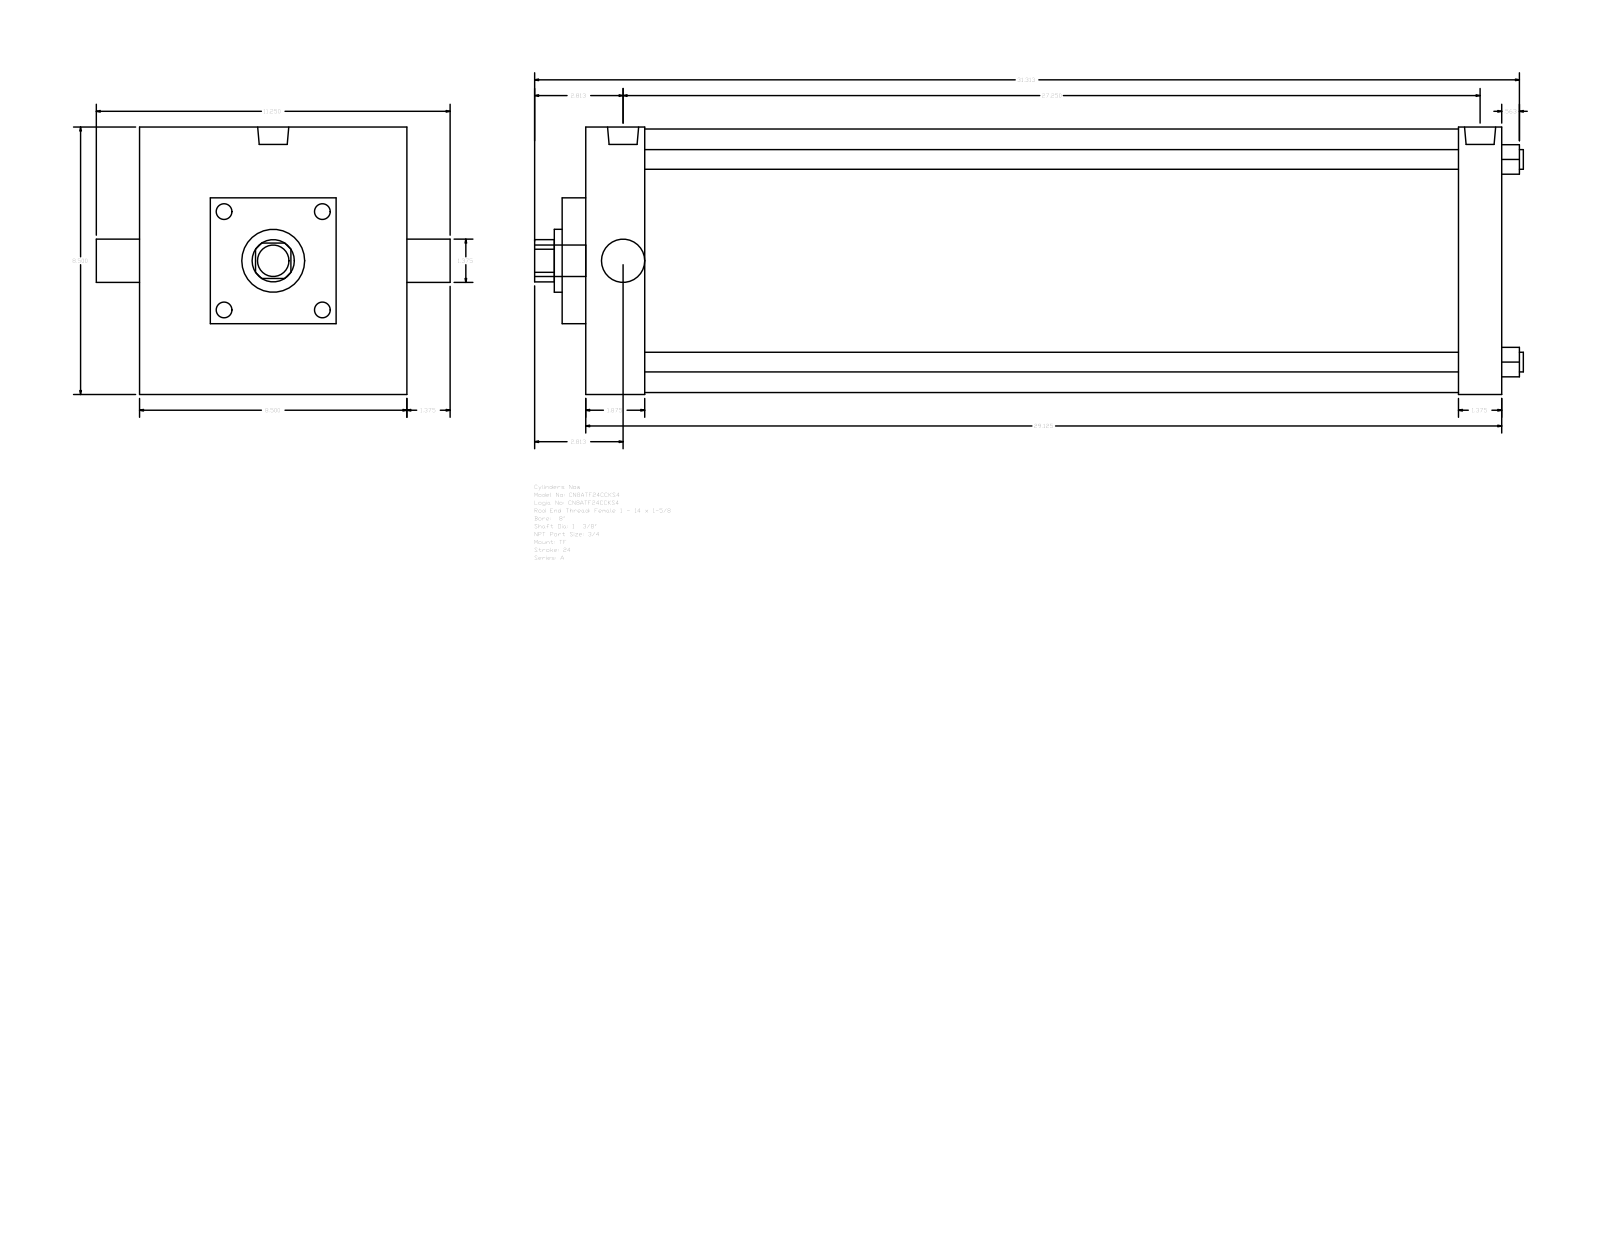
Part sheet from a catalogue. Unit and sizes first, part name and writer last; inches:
Units: inches
Overall size (bounding box): 31.437 × 11.25 × 8.5
Round holes (diameter × count): ⌀0.625 ×4, ⌀1.375 ×2, ⌀2 ×1, ⌀8.375 ×1
Round bosses / shafts (diameter × count): ⌀0.594 ×3, ⌀0.989 ×2, ⌀1 ×1
Partial cylindrical surfaces — rounded edges, fillets, slot ends (radius × count): R0.672 ×1
Main face-to-face distances: 29.125, 8.5, 1.375, 1.875, 27.25, 27.75, 25.875, 0.75, 2.625, 28.5
Hole centre spacings: 4.554, 6.44, 9.108
Bodies: 0 solids, 89 faces (65 planar, 24 cylindrical, 0 other)
Part name (STEP PRODUCT): A_TF__0800_1.375
STEP written by: GSSL Pune (CONFIG_CONTROL_DESIGN)
